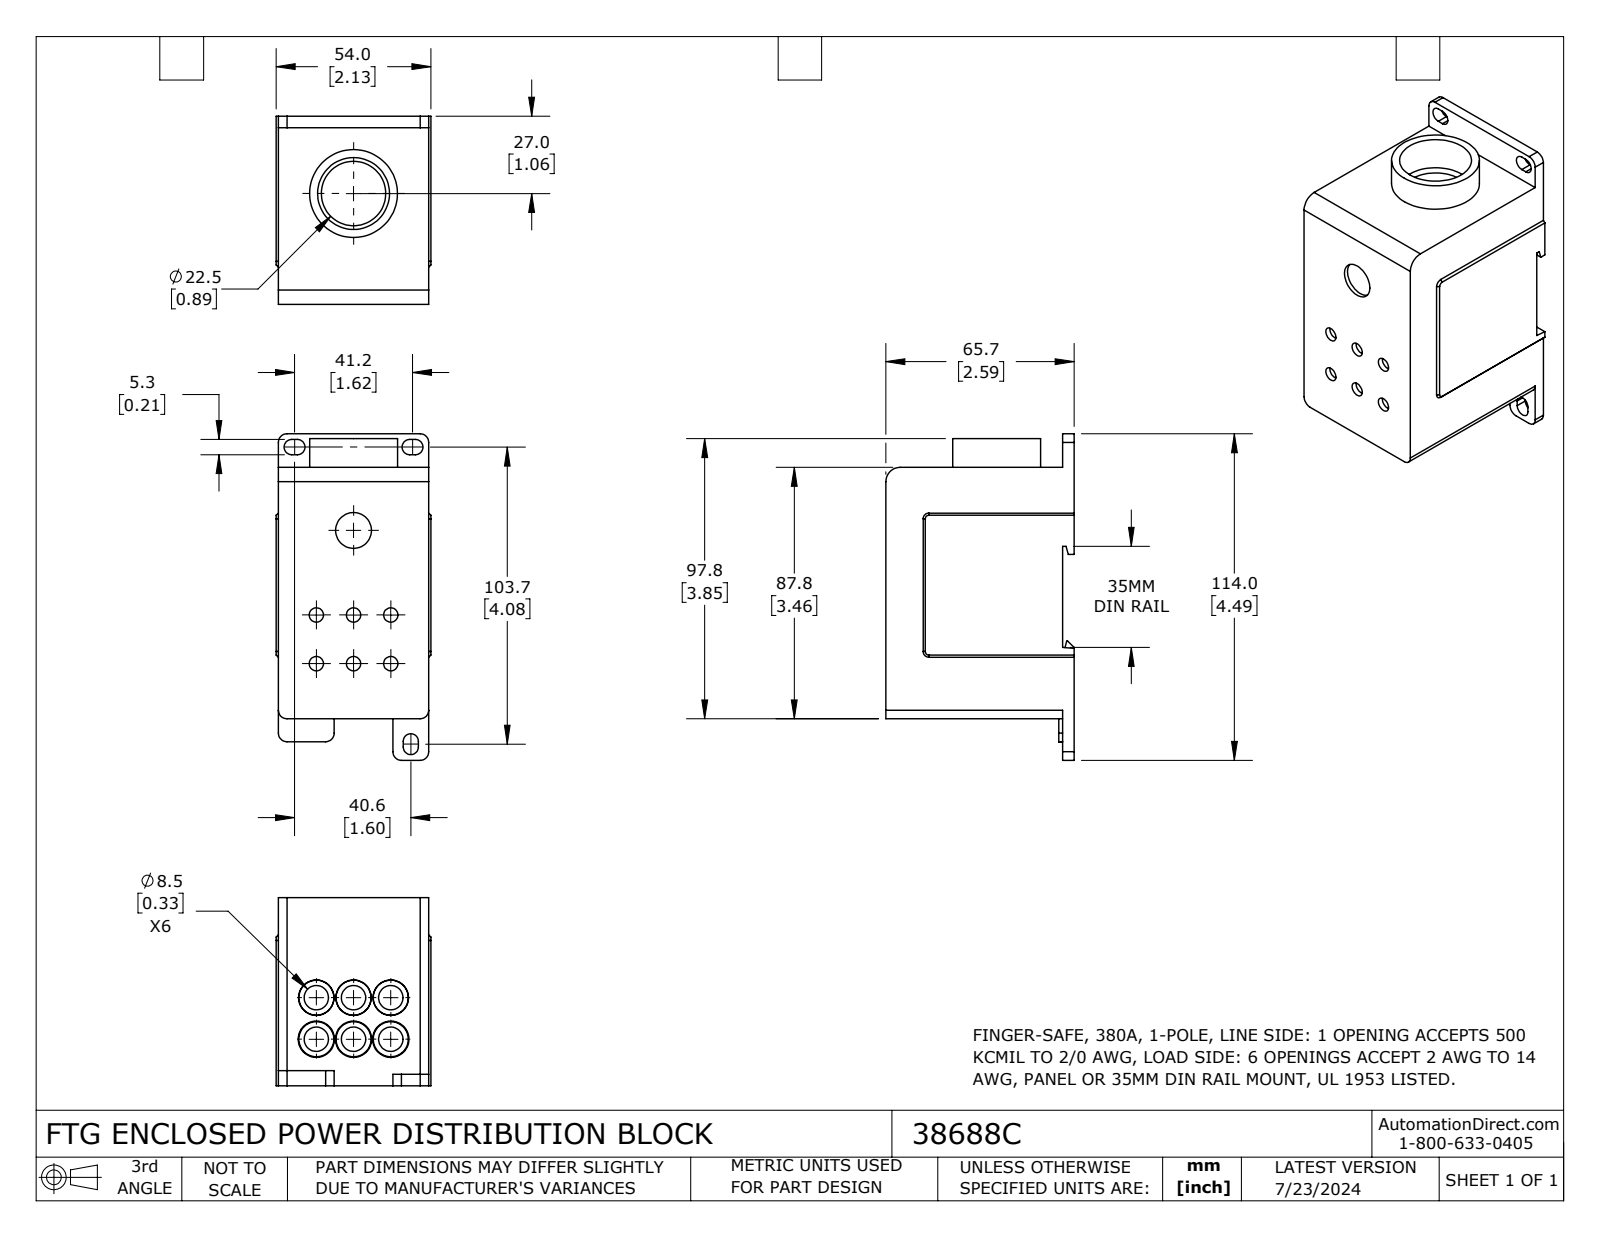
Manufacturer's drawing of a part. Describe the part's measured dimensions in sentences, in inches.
The part is named "38688C". Its 3-D file was written by "SolidWorks 2023 (CONFIG_CONTROL_DESIGN)". It is 1 solid with 146 faces: 51 planar, 50 cylindrical and 45 other. Overall it measures 4.488 by 2.587 by 2.126 inches. Its volume is 16.43 cubic inches and its surface area 64.87 square inches. Round holes: 6 of diameter 0.197, 6 of diameter 0.335, 1 of diameter 0.492, 1 of diameter 0.886, 1 of diameter 0.988. Round bosses or shafts: 1 of diameter 1.209. Partial cylindrical surfaces (rounded edges, fillets, slot ends): 8 of radius 0.118, 6 of radius 0.104, 1 of radius 0.197. The main face-to-face distances are 0.03, 2.096, 2.587, 2.067, 0.157, 2.429, 2.126, 3.457, 3.85, 0.394. The hole center spacings are 0.512, 0.767, 0.843, 1.024, 0.571, 0.669, 0.533, 0.664.
